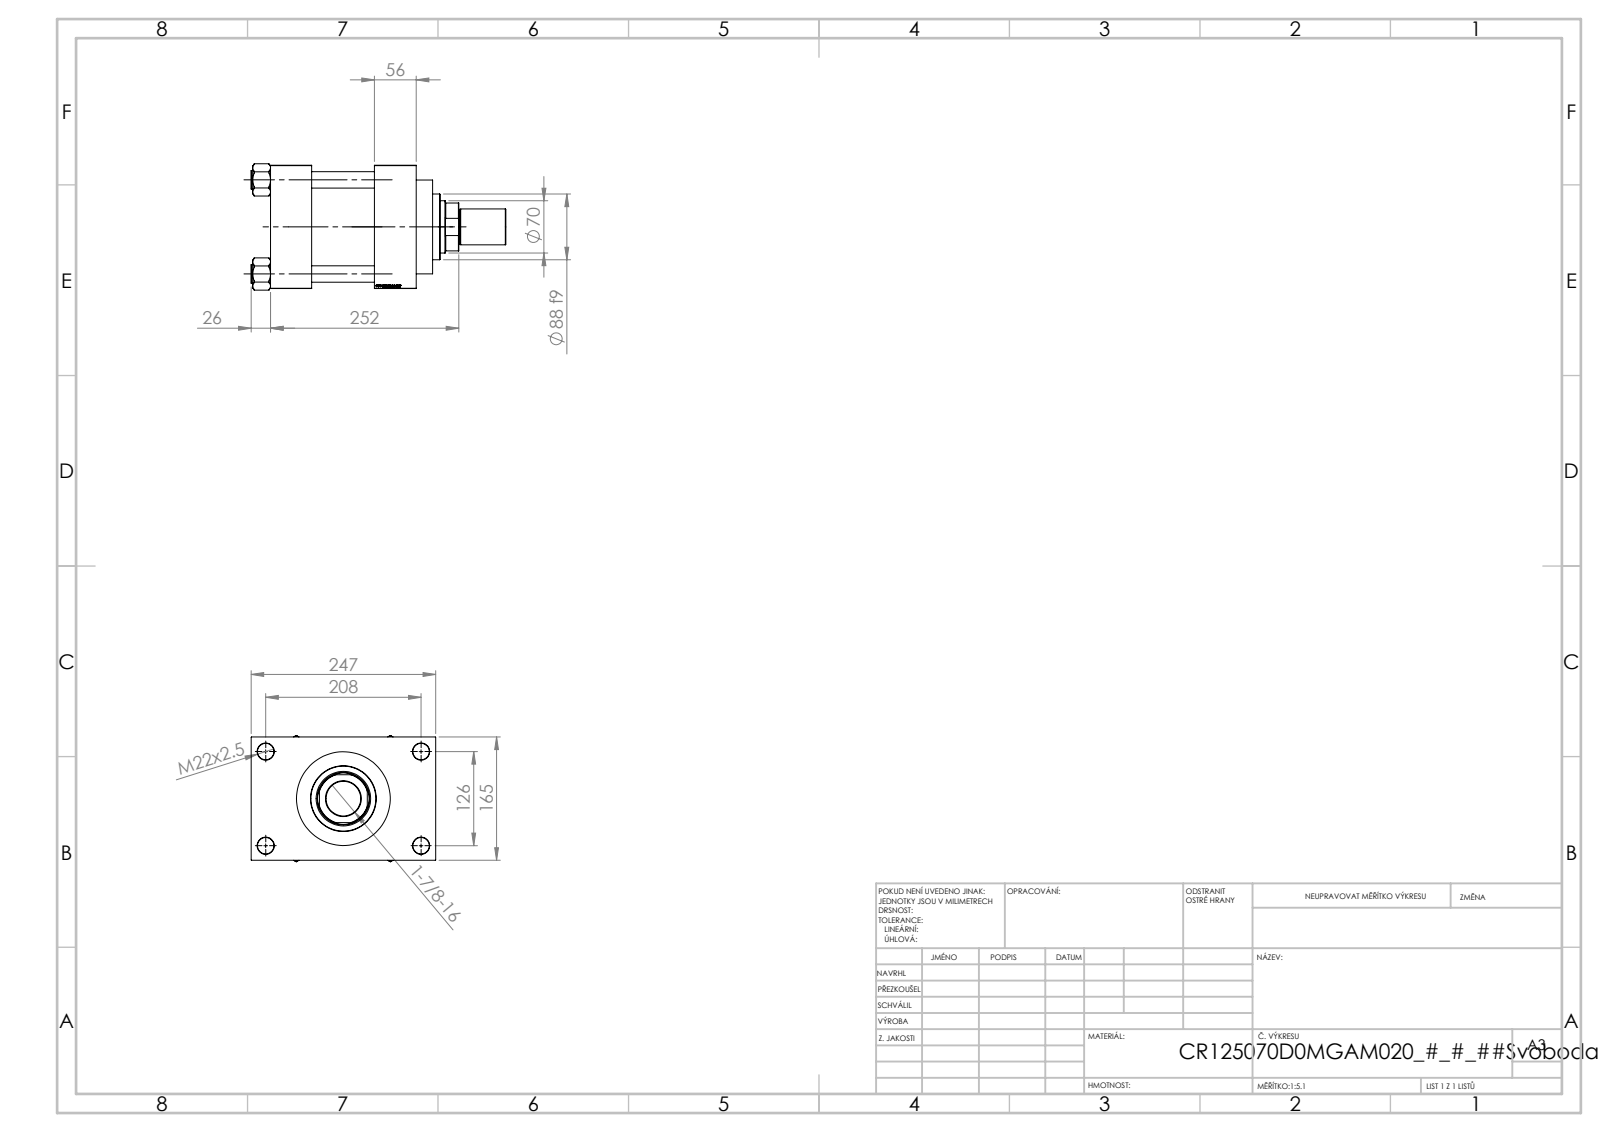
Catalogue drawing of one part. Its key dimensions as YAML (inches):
part_name: "NUT_M5_D; V215CR_VCP_D; V215CR_D_TYCINKA; ROD_END_AH (+2 more)"
step_written_by: "SolidWorks 2019 (CONFIG_CONTROL_DESIGN)"
units: inches
bodies: {solids: 12, faces: 1163, planar: 548, cylindrical: 91, other: 524}
overall_size: [13.425, 9.724, 6.659]
volume: 314.9
surface_area: 854.4
round_holes:
  - {diameter: 0.866, count: 8}
  - {diameter: 0.276, count: 2}
  - {diameter: 1.269, count: 2}
  - {diameter: 1.772, count: 2}
  - {diameter: 1.831, count: 1}
  - {diameter: 2.756, count: 1}
  - {diameter: 2.874, count: 1}
  - {diameter: 3.78, count: 1}
  - {diameter: 4.921, count: 1}
  - {diameter: 4.941, count: 1}
round_bosses_or_shafts:
  - {diameter: 0.984, count: 4}
  - {diameter: 5.157, count: 1}
  - {diameter: 3.465, count: 1}
  - {diameter: 1.89, count: 1}
  - {diameter: 1.811, count: 1}
partial_cylinders:
  - {radius: 1.339, count: 1}
face_to_face_distances: [6.496, 3.307, 2.165, 5.472, 7.677, 5.512, 2.205, 1.614, 8.11, 6.84]
hole_center_spacings: [1.616, 3.505, 4.787, 4.957, 5.215, 6.573, 8.233, 4.961]
